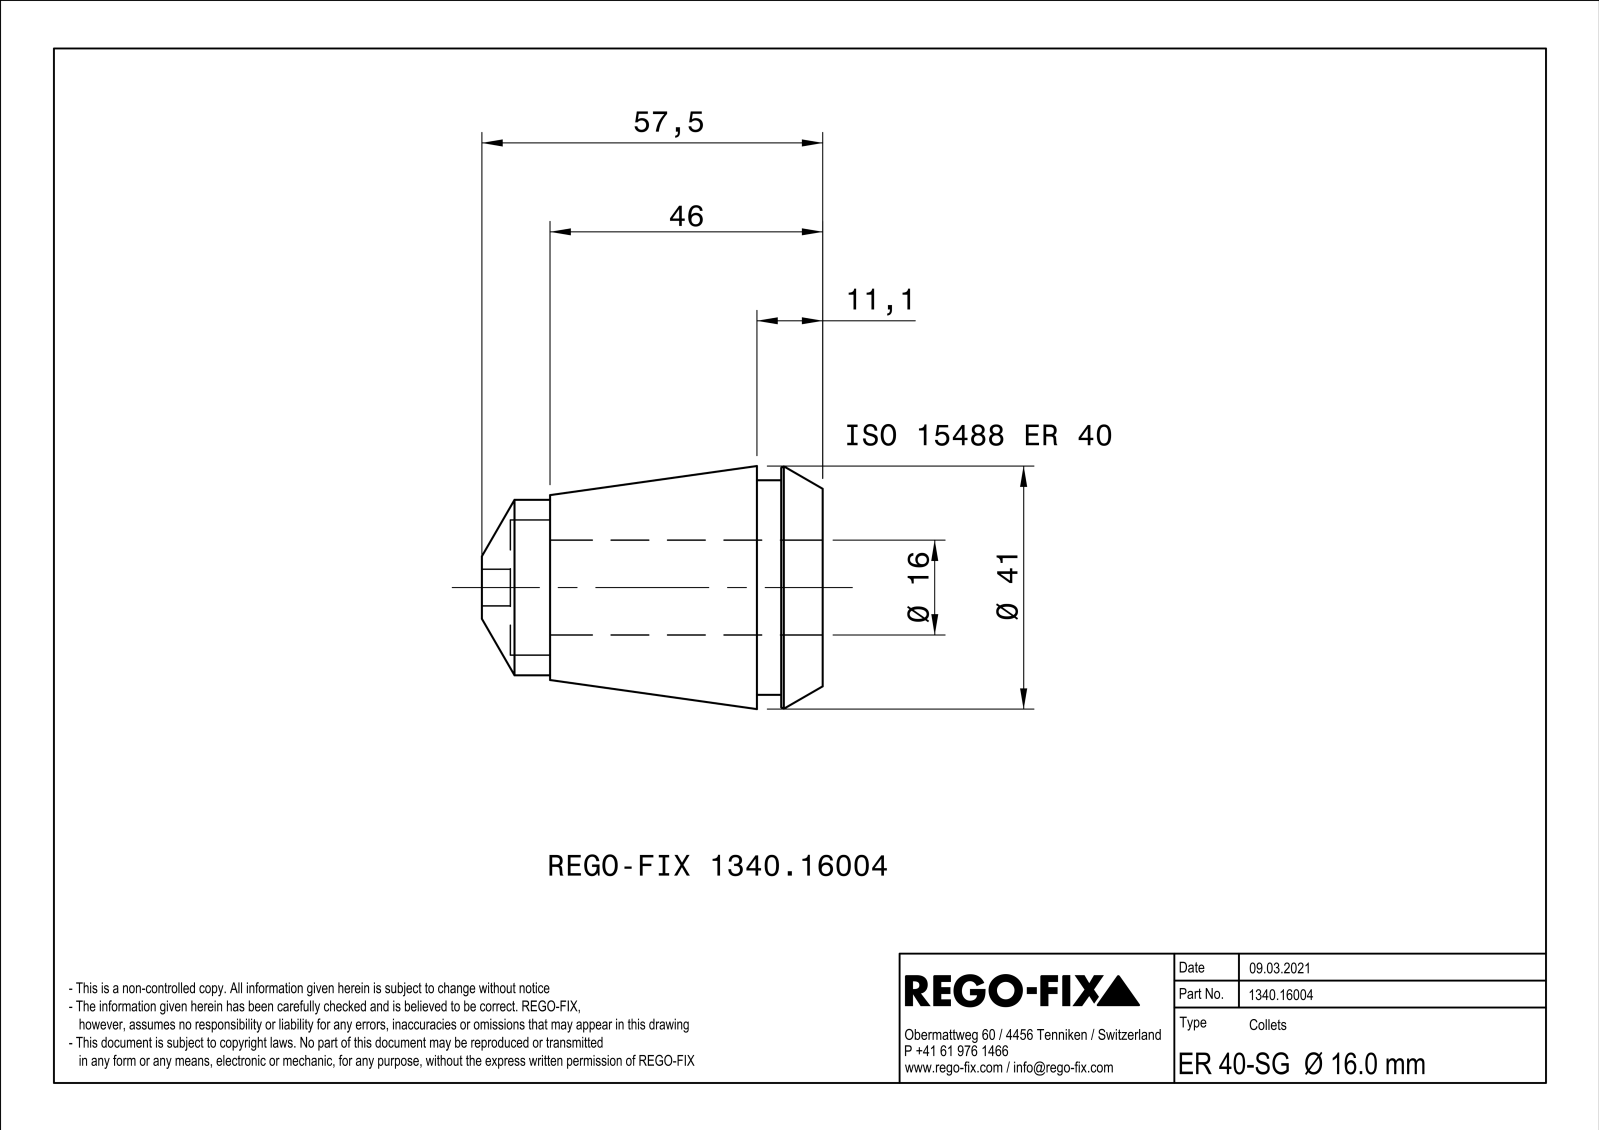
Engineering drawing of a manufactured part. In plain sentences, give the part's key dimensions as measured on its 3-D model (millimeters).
The part is named "NOCUT". Its 3-D file was written by "SIEMENS PLM Software Solid Edge ST10 (AUTOMOTIVE_DESIGN)". It is 1 solid with 283 faces: 151 planar, 36 cylindrical and 96 other. Overall it measures 61.8 by 40.85 by 40.85 millimeters. Its volume is 35 923 cubic millimeters and its surface area 22 389 square millimeters. Round holes: 1 of diameter 3, 1 of diameter 16, 1 of diameter 22.8, 1 of diameter 25, 1 of diameter 26, 1 of diameter 28.2. Round bosses or shafts: 1 of diameter 36.2, 1 of diameter 29.6, 1 of diameter 25.8, 1 of diameter 25.5, 1 of diameter 24.8, 1 of diameter 7, 1 of diameter 4.4. Partial cylindrical surfaces (rounded edges, fillets, slot ends): 1 of radius 3.09. The main face-to-face distances are 1, 52.7, 44, 8.7, 7, 37, 45.7, 4.1, 11.1, 32.9.
